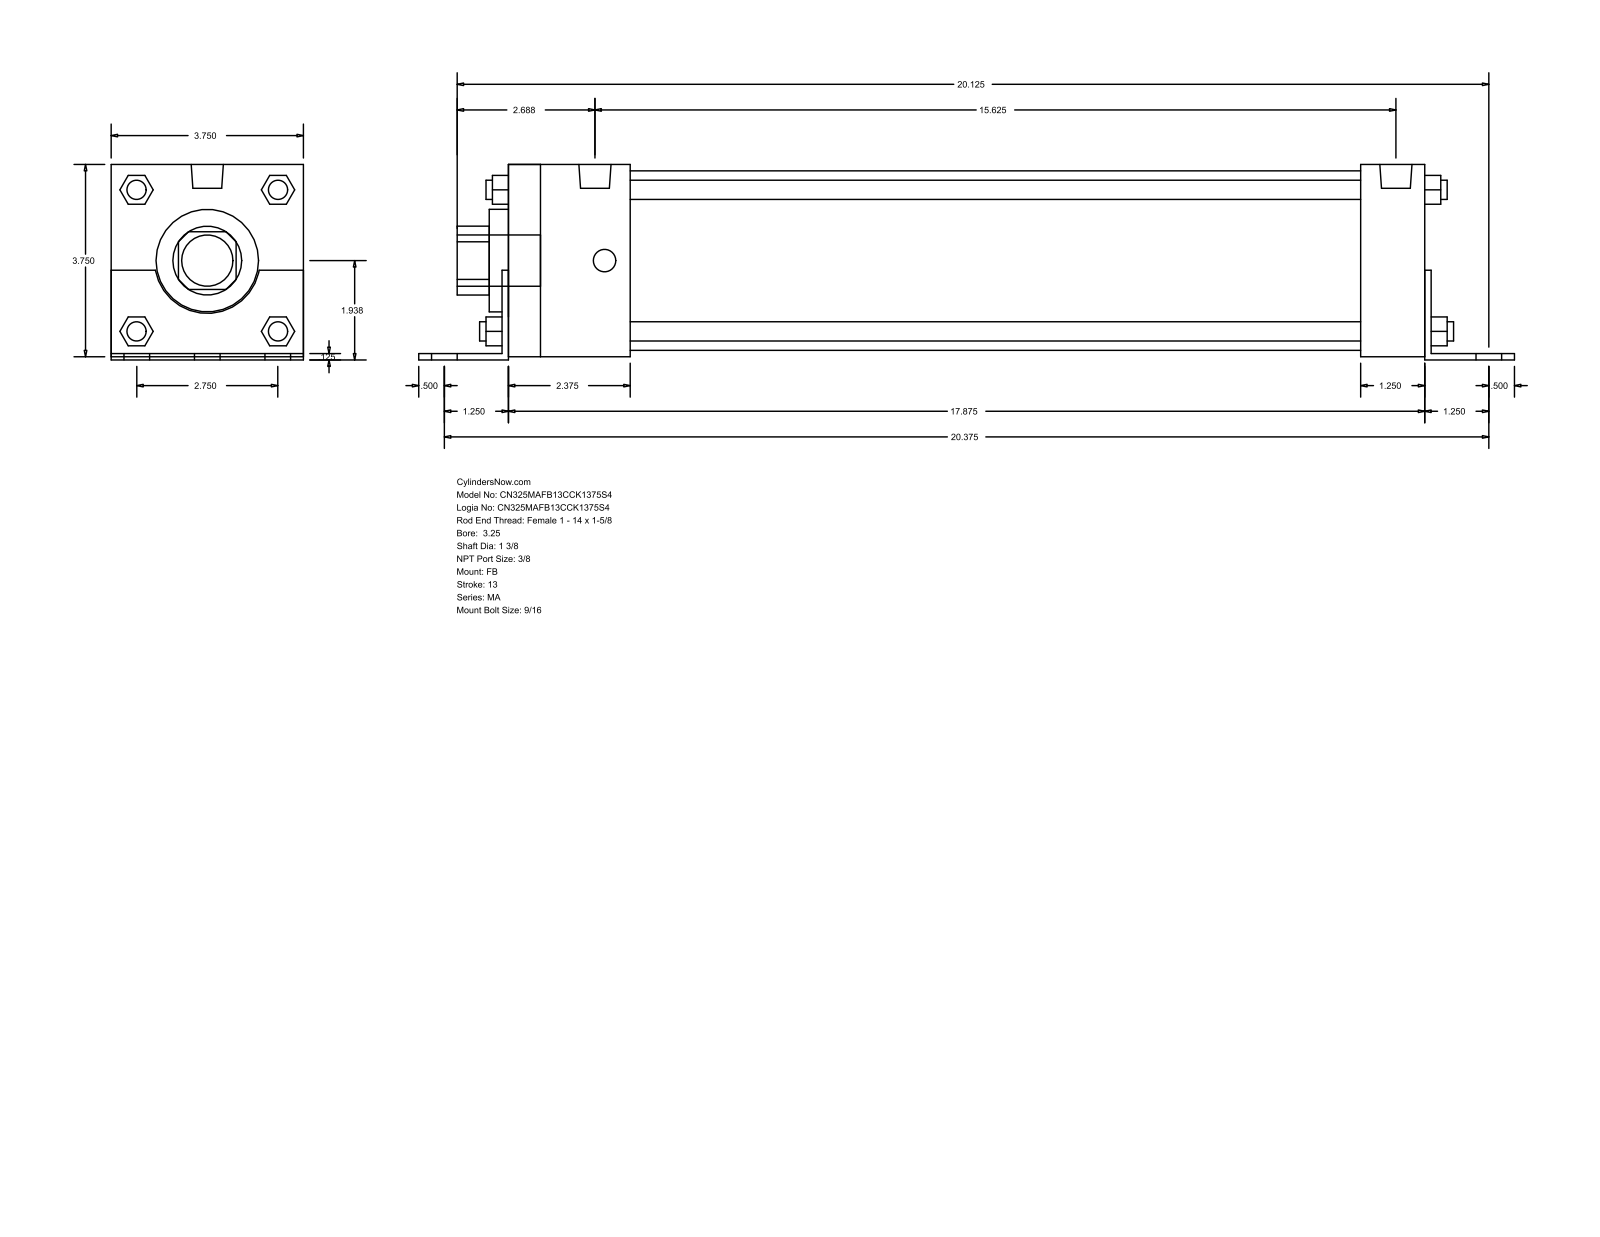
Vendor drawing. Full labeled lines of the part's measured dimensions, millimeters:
Part name (STEP PRODUCT): MA_FB__0325_1.375
STEP written by: GSSL Pune (CONFIG_CONTROL_DESIGN)
Units: millimetres
Bodies: 0 solids, 140 faces (105 planar, 35 cylindrical, 0 other)
Overall size (bounding box): 542.92 × 96.84 × 95.25
Round holes (diameter × count): ⌀34.92 ×1, ⌀50.8 ×1, ⌀88.9 ×1
Round bosses / shafts (diameter × count): ⌀14.29 ×6, ⌀11.11 ×4, ⌀9.53 ×4, ⌀15.93 ×2, ⌀25.4 ×1
Partial cylindrical surfaces — rounded edges, fillets, slot ends (radius × count): R17.06 ×1, R26.16 ×1
Main face-to-face distances: 95.24, 3.17, 1.59, 96.83, 1.58, 93.66, 457.2, 454.03, 31.75, 60.32
